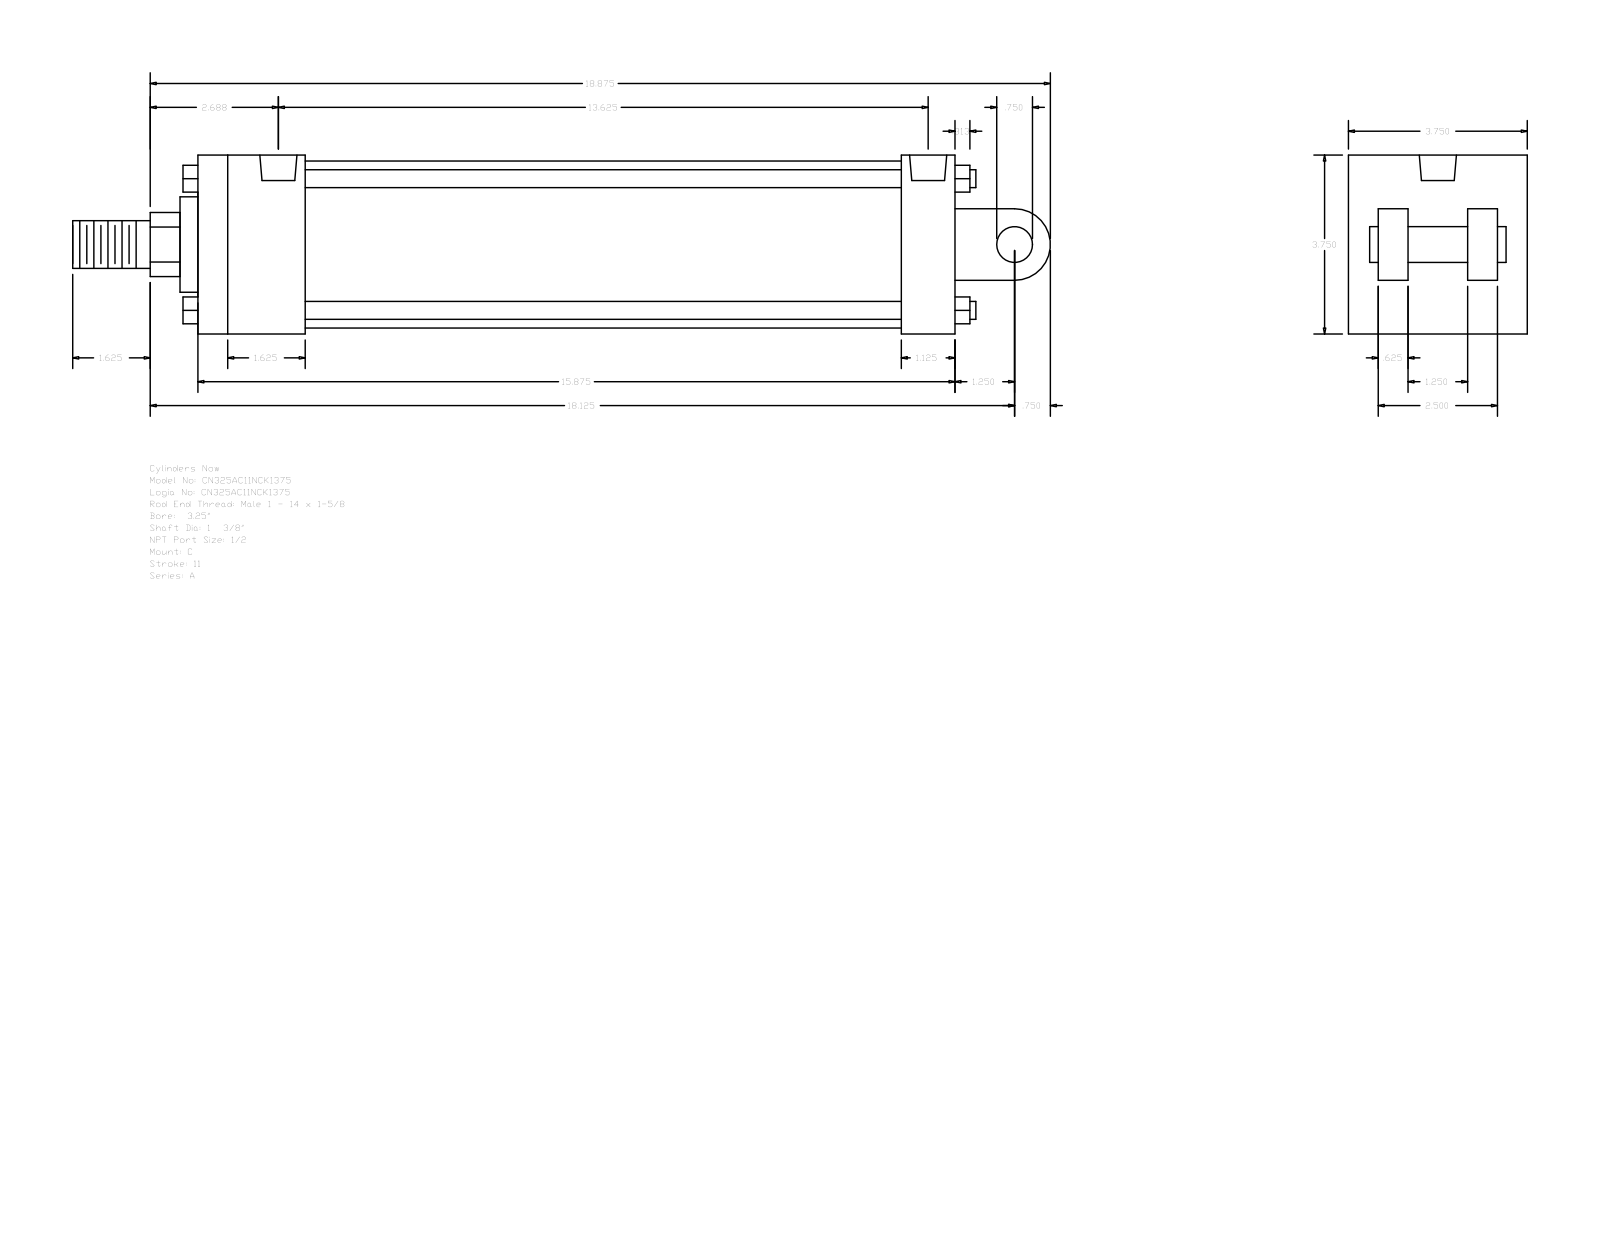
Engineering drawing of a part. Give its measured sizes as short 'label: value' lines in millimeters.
name: A_C__0325_1.375
written by: GSSL Pune (CONFIG_CONTROL_DESIGN)
unit: mm
bodies: 0 solids, 135 faces (102 planar, 33 cylindrical, 0 other)
size: 520.7 × 95.25 × 95.25
holes: 4× ⌀8.73, 2× ⌀19.77
bosses: 4× ⌀9.53, 1× ⌀88.9, 1× ⌀50.8, 1× ⌀34.92, 1× ⌀25.4, 1× ⌀19.05
rounds: 1× R17.06, 1× R19.05
face distances: 95.24, 403.22, 15.87, 28.57, 63.5, 66.67, 57.15, 79.37, 31.74, 47.63
hole spacings: 3.18, 339.72, 342.9, 346.08
